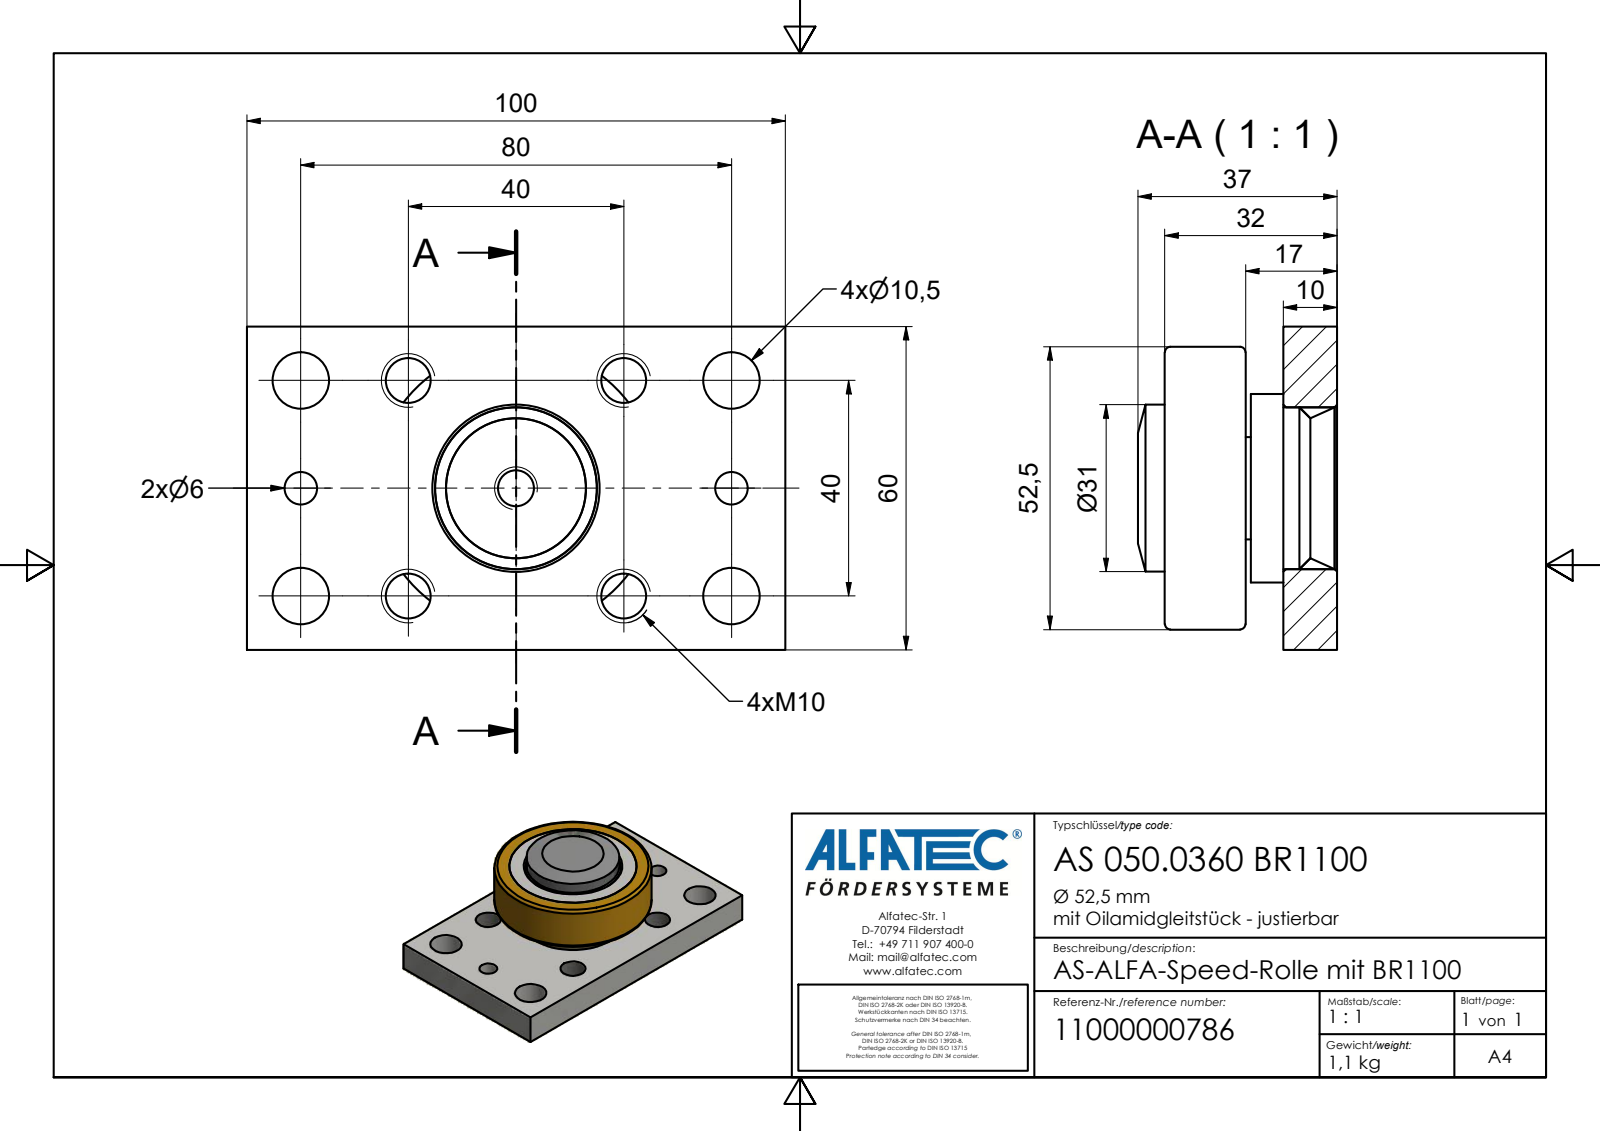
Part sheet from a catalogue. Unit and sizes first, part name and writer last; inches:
Units: inches
Overall size (bounding box): 3.937 × 2.362 × 1.457
Round holes (diameter × count): ⌀0.33 ×4, ⌀0.413 ×4, ⌀0.236 ×2, ⌀0.262 ×1
Round bosses / shafts (diameter × count): ⌀2.067 ×1, ⌀1.378 ×1, ⌀1.22 ×1, ⌀0.748 ×1
Main face-to-face distances: 0.394, 0.669, 0.276, 0.63, 1.26, 0.866, 0.591, 2.362, 0.236, 0.039
Hole centre spacings: 0.787, 1.113, 1.575, 1.761, 2.362, 2.49, 2.839, 3.246
Volume: 5.824 in³ · Surface area: 37.35 in²
Bodies: 1 solid, 30 faces (12 planar, 15 cylindrical, 3 other)
Part name (STEP PRODUCT): AS 050.0360.BR_Konturvereinfachung_1
STEP written by: Autodesk Inventor 2012 (AUTOMOTIVE_DESIGN)
